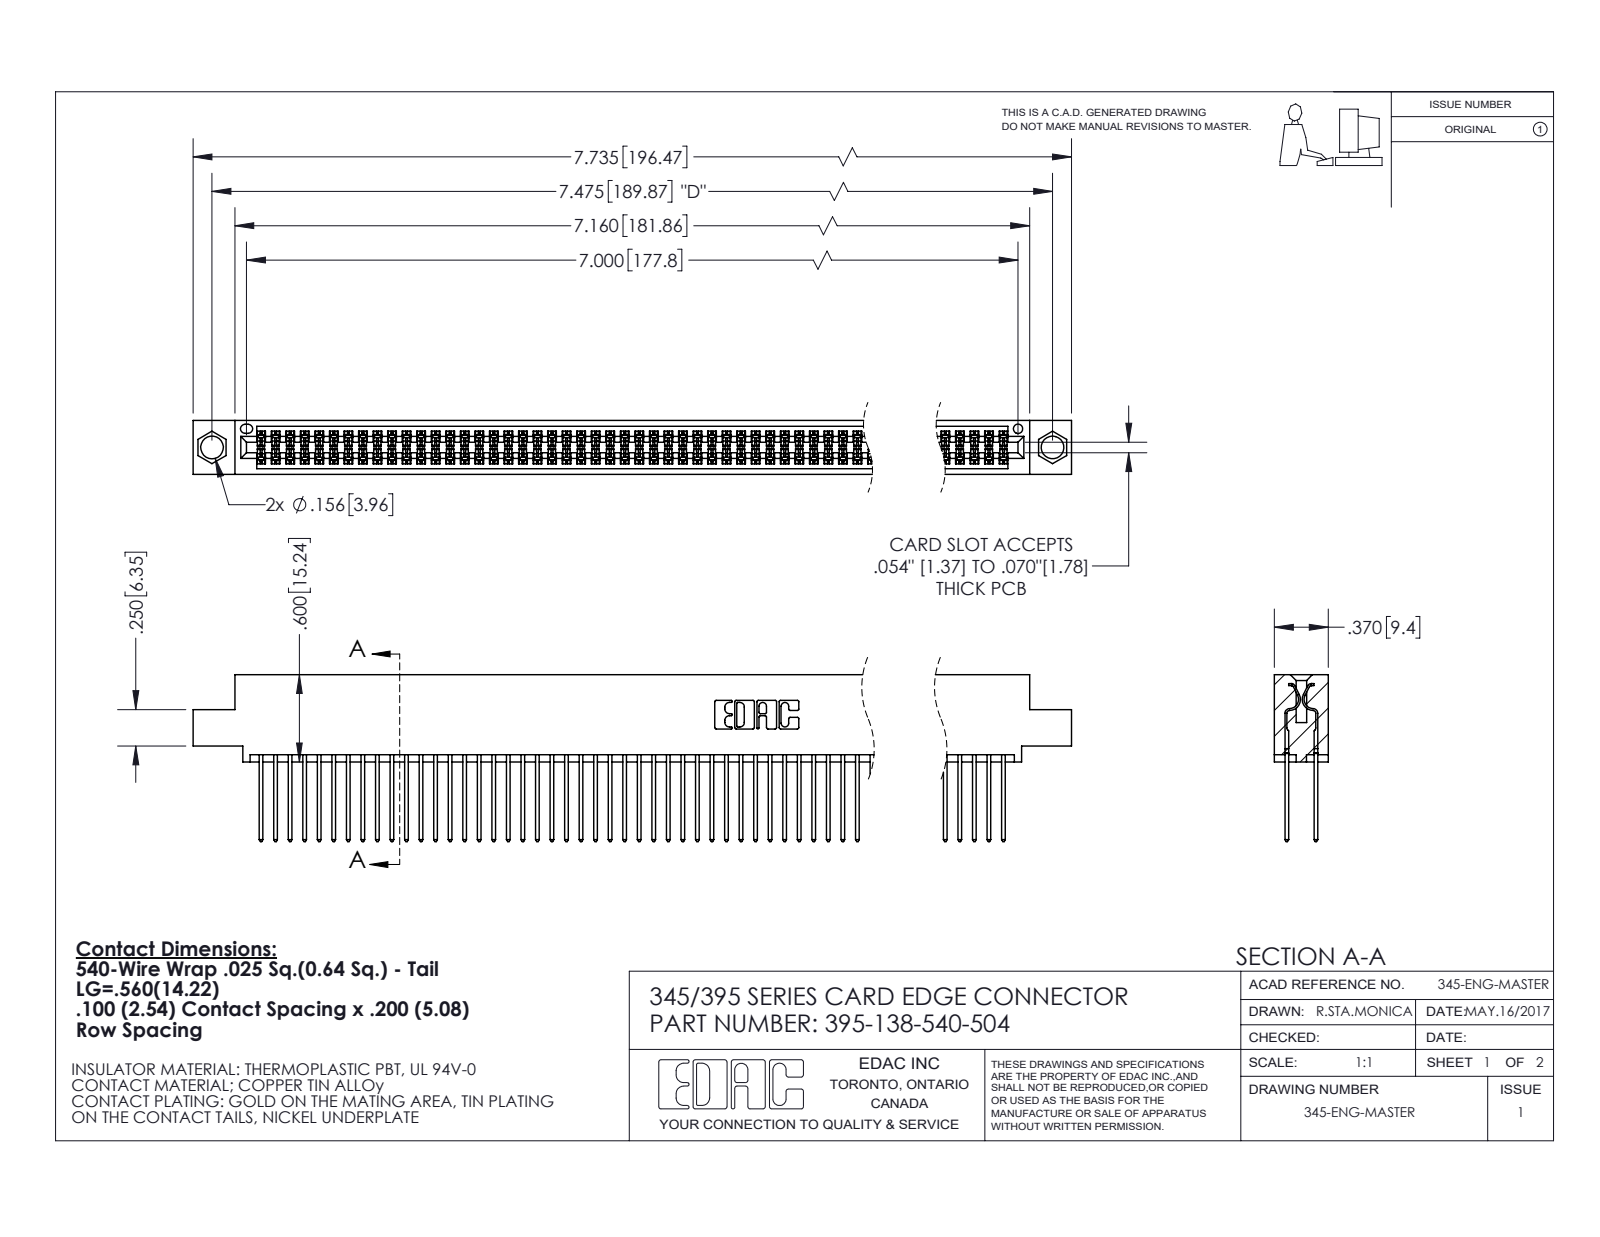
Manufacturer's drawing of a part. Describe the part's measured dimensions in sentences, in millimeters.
The part is named "395-138-540-504; 345 Part_0.110 Offset - 0.156 Dia-TI; 345-292-001_345-293-140". Its 3-D file was written by "SolidWorks 2020 (CONFIG_CONTROL_DESIGN)". It is 139 solids with 7044 faces: 4652 planar, 2392 cylindrical and 0 other. Overall it measures 196.5 by 29.1 by 9.4 millimeters. Its volume is 19 680 cubic millimeters and its surface area 31 990 square millimeters. Round holes: 2 of diameter 4, 1 of diameter 1.6. Partial cylindrical surfaces (rounded edges, fillets, slot ends): 207 of radius 0.2, 138 of radius 0.3, 22 of radius 0.3, 6 of radius 0.2, 6 of radius 0.8, 3 of radius 0.7, 2 of radius 0.4, 2 of radius 0.5. The main face-to-face distances are 7.6, 1.8, 5.1, 2.5, 6.9, 0.6, 5.7, 9.4, 4.4, 3.8. The hole center spacings are 6.9, 183.9, 189.9.
